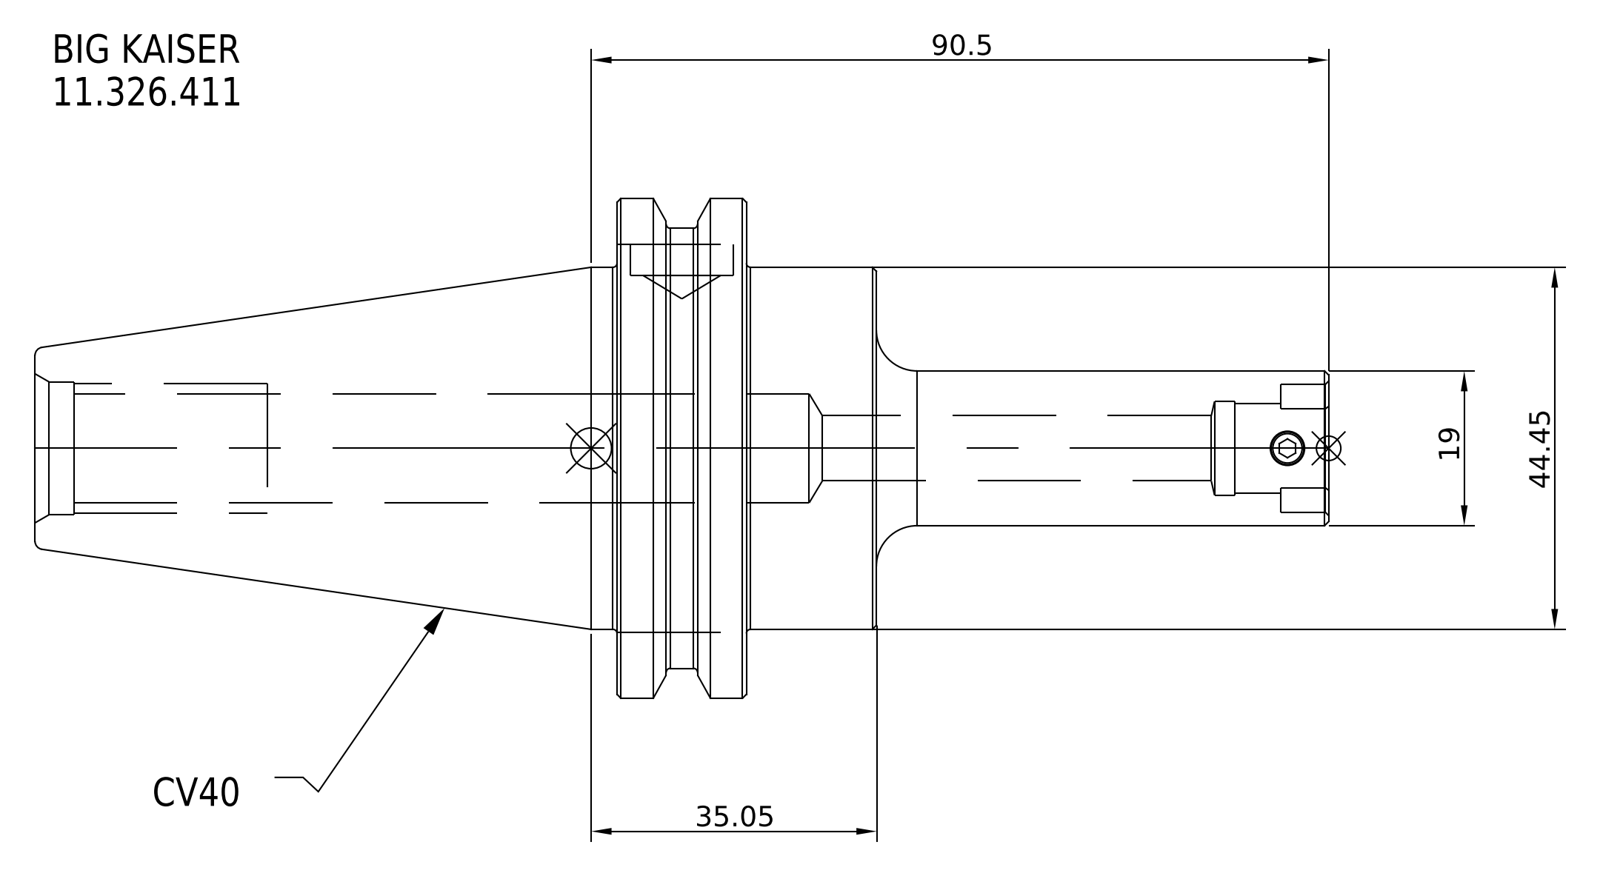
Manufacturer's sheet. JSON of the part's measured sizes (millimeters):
{"part_name": "11_326_411", "step_written_by": "SolidWorks 2021 (CONFIG_CONTROL_DESIGN)", "units": "millimeters", "bodies": {"solids": 1, "faces": 27, "planar": 7, "cylindrical": 12, "other": 8}, "overall_size": [158.75, 63.5, 63.5], "volume_mm3": 158223, "surface_area_mm2": 22551, "round_bosses_or_shafts": [[63.5, 1], [56.36, 1], [44.45, 1], [19, 1]], "face_to_face_distances": [15.88, 16, 31.88, 103.3, 87.3, 71.42, 77.45, 81.3, 55.45, 71.45]}
